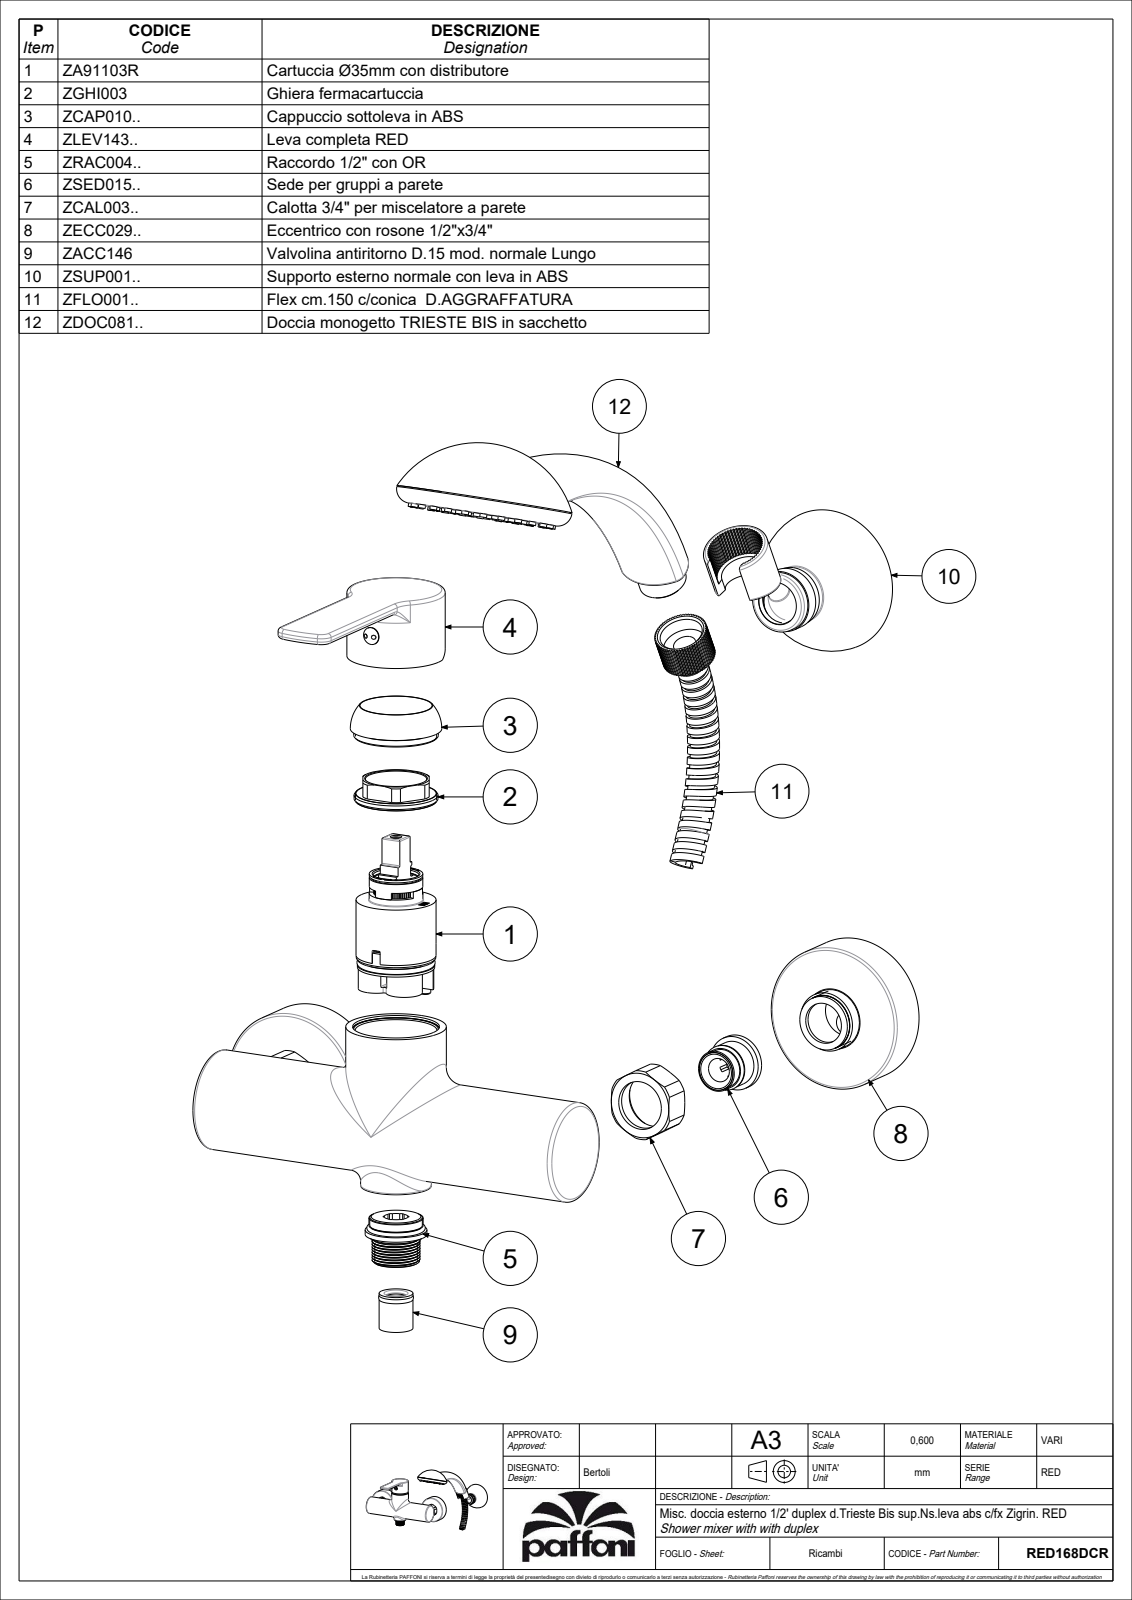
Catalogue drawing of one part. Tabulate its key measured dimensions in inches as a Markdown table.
| quantity | value |
| --- | --- |
| part name | RED168DCR |
| STEP written by | CREO PARAMETRIC BY PTC INC, 2020044 (CONFIG_CONTROL_DESIGN) |
| units | inches |
| bodies | 2 solids, 2333 faces (1134 planar, 768 cylindrical, 431 other) |
| overall size | 13.602 × 11.003 × 7.888 |
| volume | 24.89 in³ |
| surface area | 307.6 in² |
| round holes (diameter × count) | 0.059 × 48, 0.354 × 3, 0.472 × 3, 0.709 × 3, 0.13 × 2, 0.157 × 2, 0.276 × 2, 0.315 × 2, 0.413 × 2, 0.591 × 2, 0.807 × 2, 0.846 × 2 |
| round bosses / shafts (diameter × count) | 0.118 × 48, 1.063 × 4, 2.5 × 2, 1.732 × 2, 0.945 × 2, 0.776 × 2, 0.354 × 2, 2.953 × 1 |
| partial cylindrical surfaces (radius × count) | 0.02 × 83, 0.006 × 11, 0.012 × 9, 0.039 × 4, 0.059 × 4, 0.276 × 4, 0.394 × 4, 0.197 × 2 |
| main face-to-face distances | 0.024, 2.697, 1.083, 4.429, 0.177, 0.128, 6.998, 2.569, 4.301, 0.118 |
| hole center spacings | 1.169, 0.411, 0.967, 0.591, 0.633, 0.786, 0.919, 1.12 |
